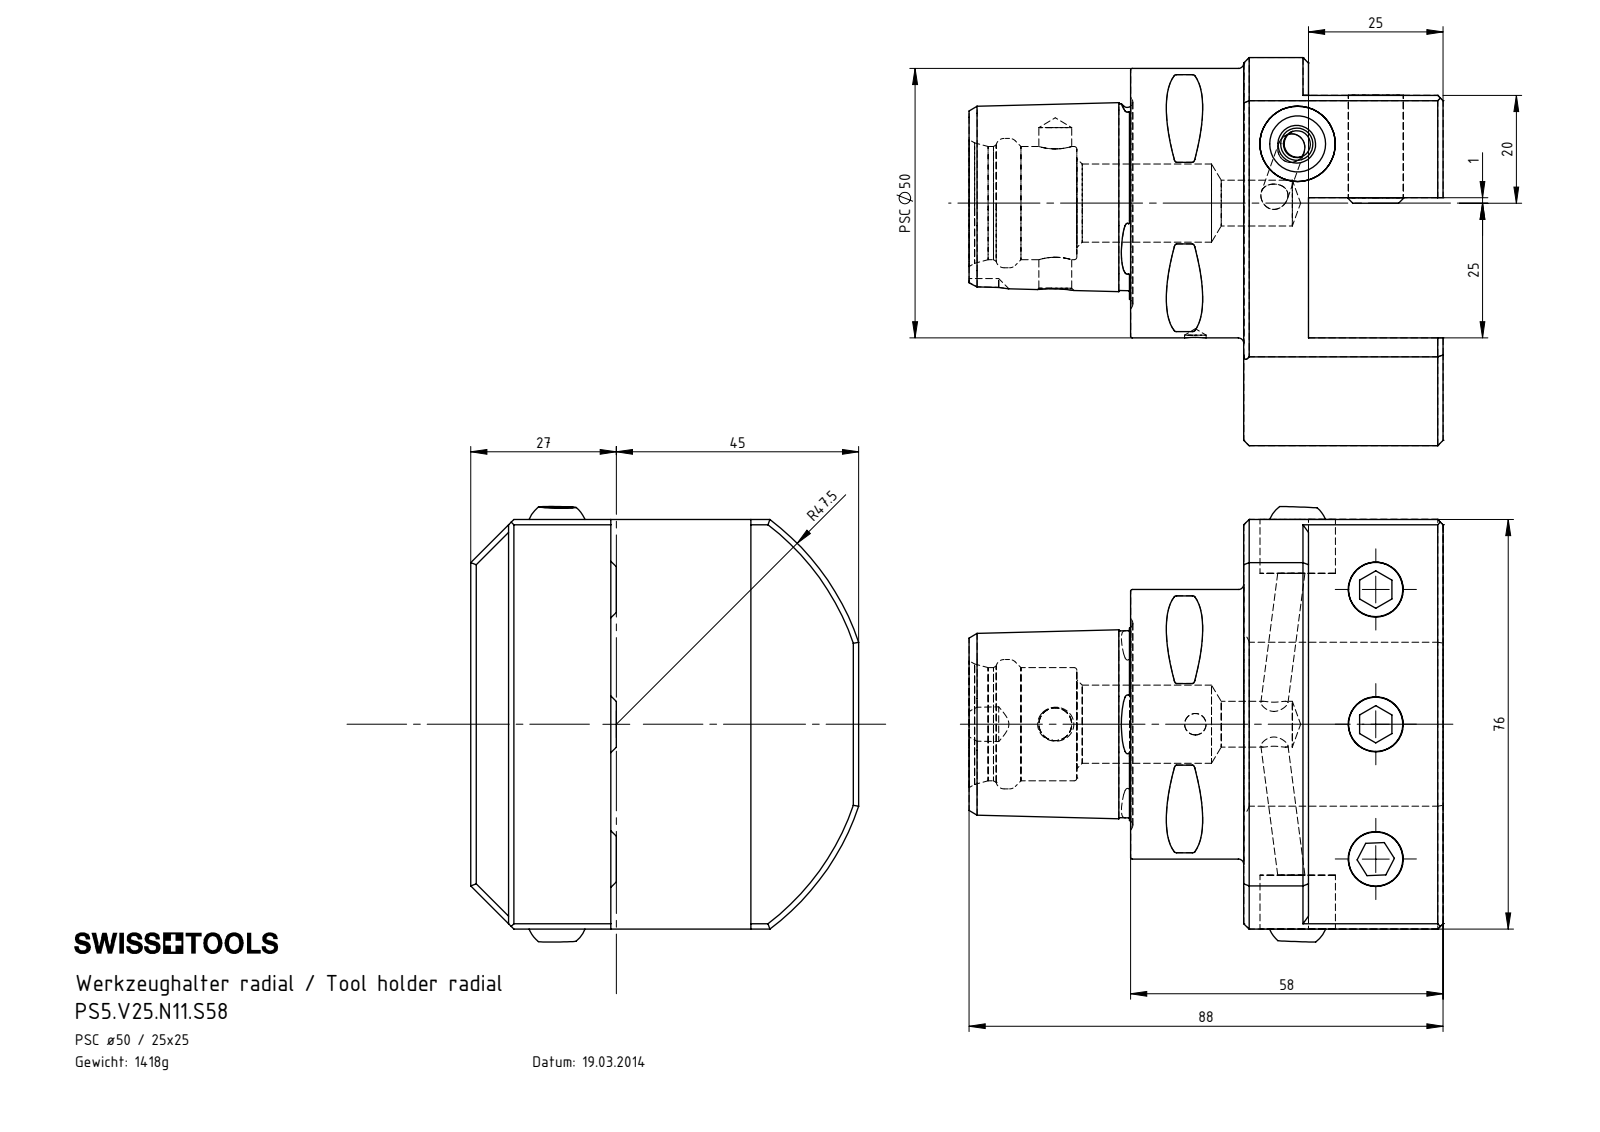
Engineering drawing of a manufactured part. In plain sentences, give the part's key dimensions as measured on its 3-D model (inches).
The part is named "KU1-U14.001.012; KU1-U14.001.012_2; KU1-U14.001.012_1; PS5-V25.N11.S58_A (+2 more)". Its 3-D file was written by "SolidWorks 2017 (AUTOMOTIVE_DESIGN)". It is 8 solids with 235 faces: 67 planar, 61 cylindrical and 107 other. Overall it measures 3.465 by 3.181 by 2.835 inches. Its volume is 11.11 cubic inches and its surface area 63.12 square inches. Round holes: 4 of diameter 0.197, 3 of diameter 0.402, 1 of diameter 0.157, 1 of diameter 0.24, 1 of diameter 0.335, 1 of diameter 0.394, 1 of diameter 0.551, 1 of diameter 0.571, 1 of diameter 0.827, 1 of diameter 0.945. Round bosses or shafts: 3 of diameter 0.472, 1 of diameter 1.969. Partial cylindrical surfaces (rounded edges, fillets, slot ends): 8 of radius 0.02, 1 of radius 0.157, 1 of radius 1.87. The main face-to-face distances are 1.457, 0.984, 0.472, 1.024, 1.772, 0.748, 0.787, 1.811, 2.559, 2.992. The hole center spacings are 0.984, 1.646, 2.541, 1.024, 1.319, 1.969, 2.343.
